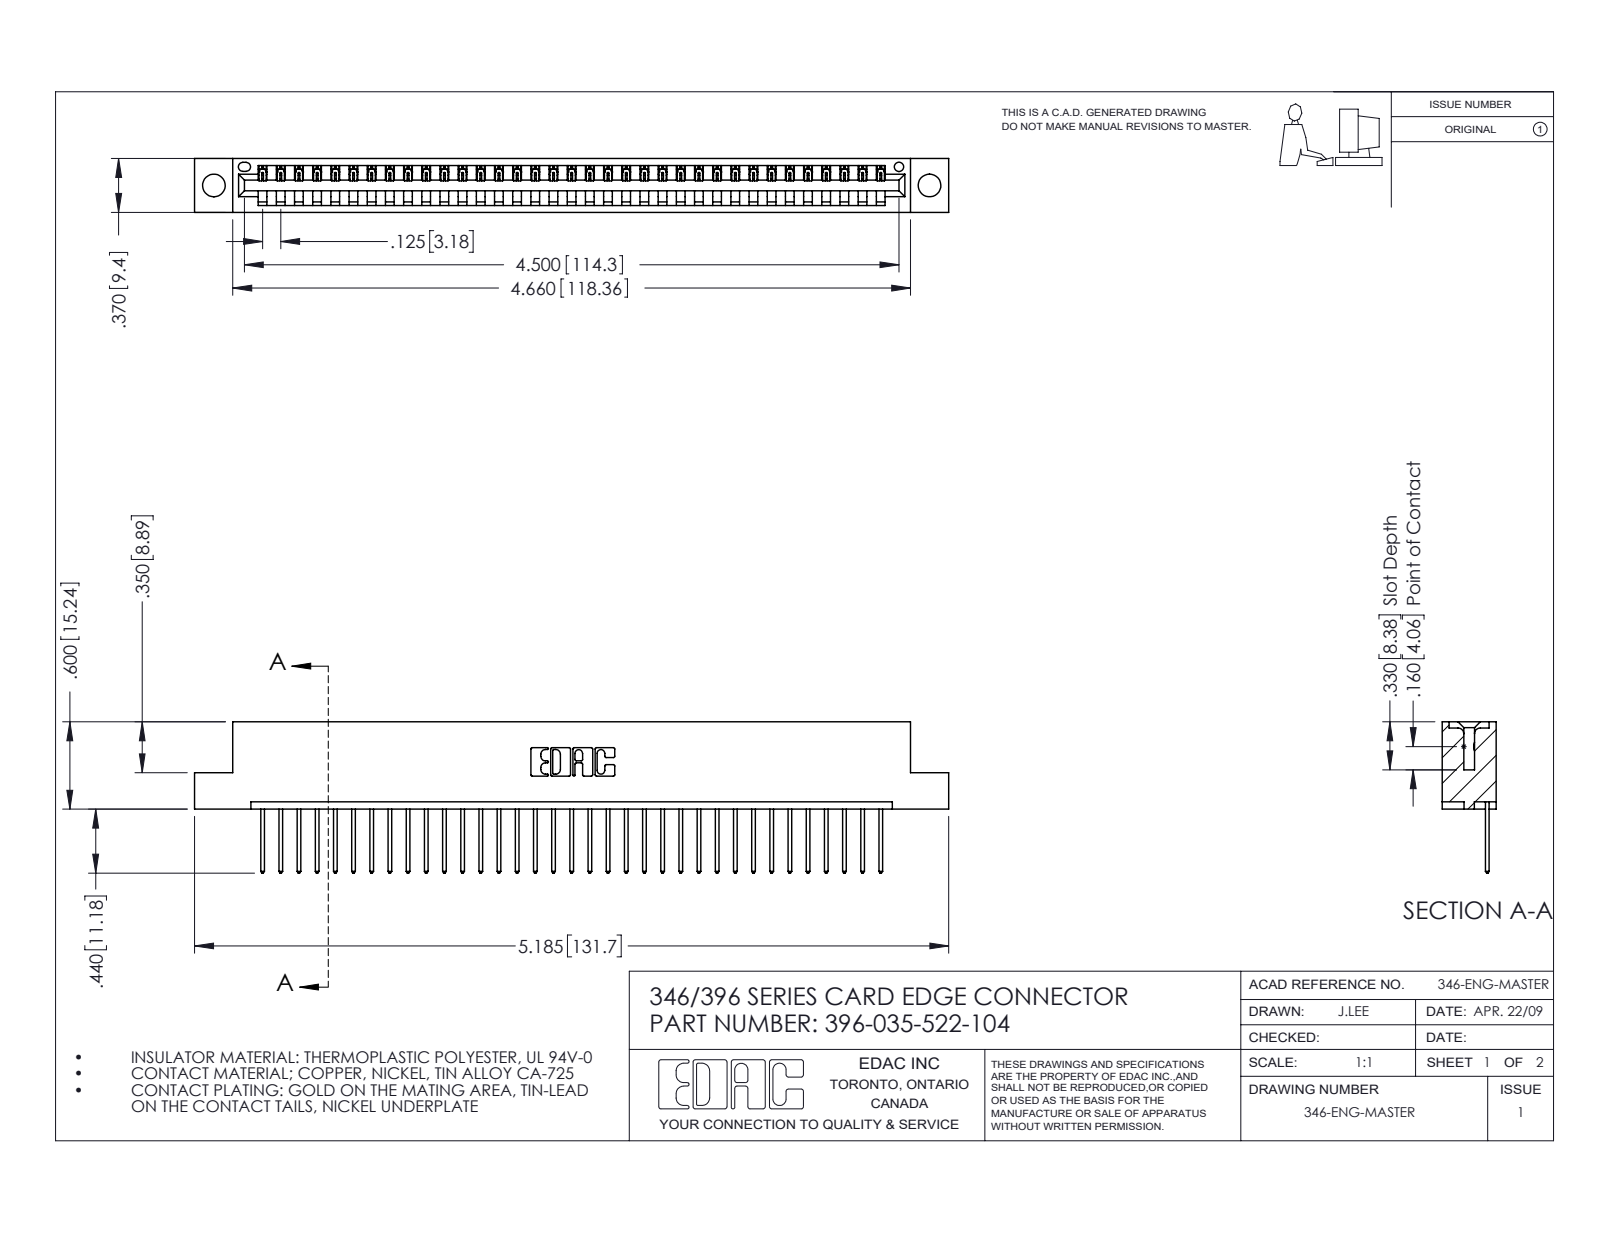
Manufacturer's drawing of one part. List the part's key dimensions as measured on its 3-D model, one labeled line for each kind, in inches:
Part name (STEP PRODUCT): 345-292-001_345-293-122; 346 Part_Flush Mounting Lugs - 0.156 Dia-TH; 396-035-522-104
STEP written by: SolidWorks 2016 (CONFIG_CONTROL_DESIGN)
Units: inches
Bodies: 36 solids, 2152 faces (1476 planar, 676 cylindrical, 0 other)
Overall size (bounding box): 5.185 × 1.04 × 0.37
Volume: 0.761 in³ · Surface area: 23.95 in²
Round holes (diameter × count): ⌀0.156 ×2, ⌀0.064 ×1
Partial cylindrical surfaces — rounded edges, fillets, slot ends (radius × count): R0.006 ×70, R0.01 ×70, R0.01 ×22, R0.007 ×6, R0.031 ×6, R0.026 ×3, R0.031 ×2, R0.04 ×2
Main face-to-face distances: 0.048, 0.322, 0.37, 0.25, 0.072, 0.298, 0.025, 0.148, 0.222, 0.1
Hole centre spacings: 0.246, 4.711, 4.92
